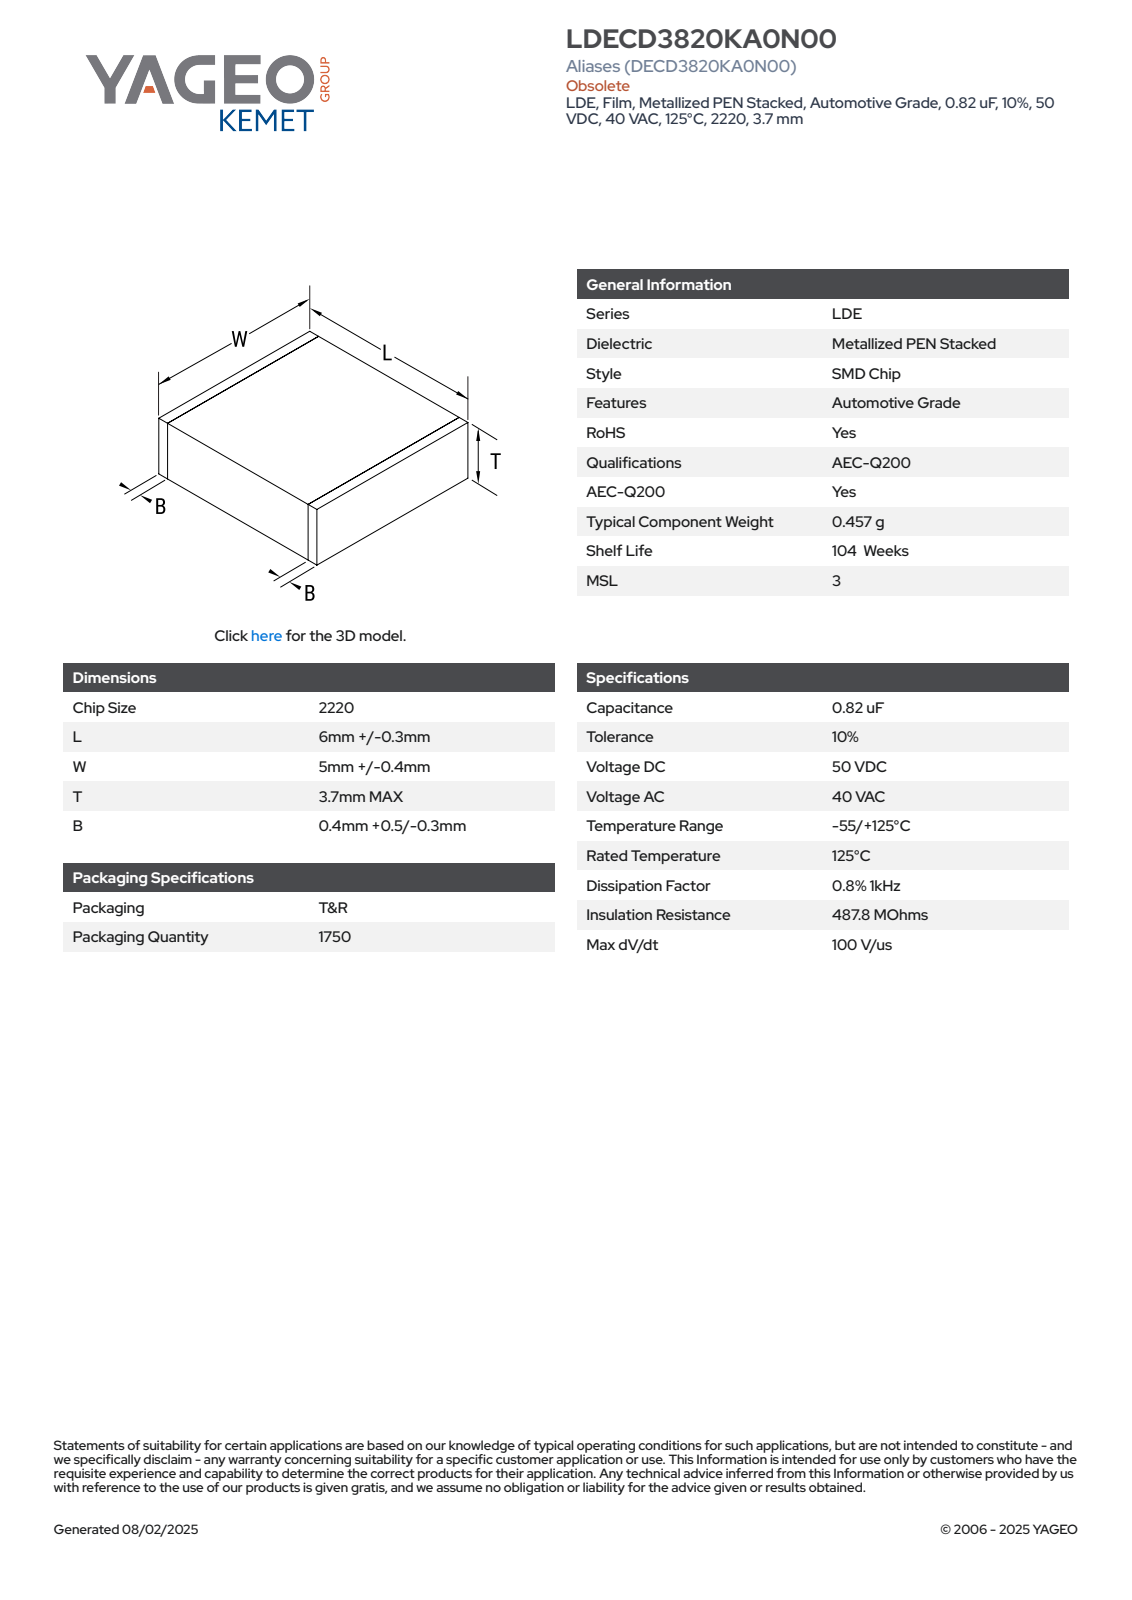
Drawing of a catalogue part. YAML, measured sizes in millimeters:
part_name: "CFS_LDELDB_2220_L6.3W5.4T3.7B0.9"
step_written_by: "SolidWorks 2020 (AUTOMOTIVE_DESIGN)"
units: millimeters
bodies: {solids: 4, faces: 73, planar: 73, cylindrical: 0, other: 0}
overall_size: [6.3, 5.4, 3.7]
volume: 125
surface_area: 156
face_to_face_distances: [3.68, 6.3, 5.38, 3.69, 5.39, 3.7, 5.4, 0.5, 5.8, 5.3]
